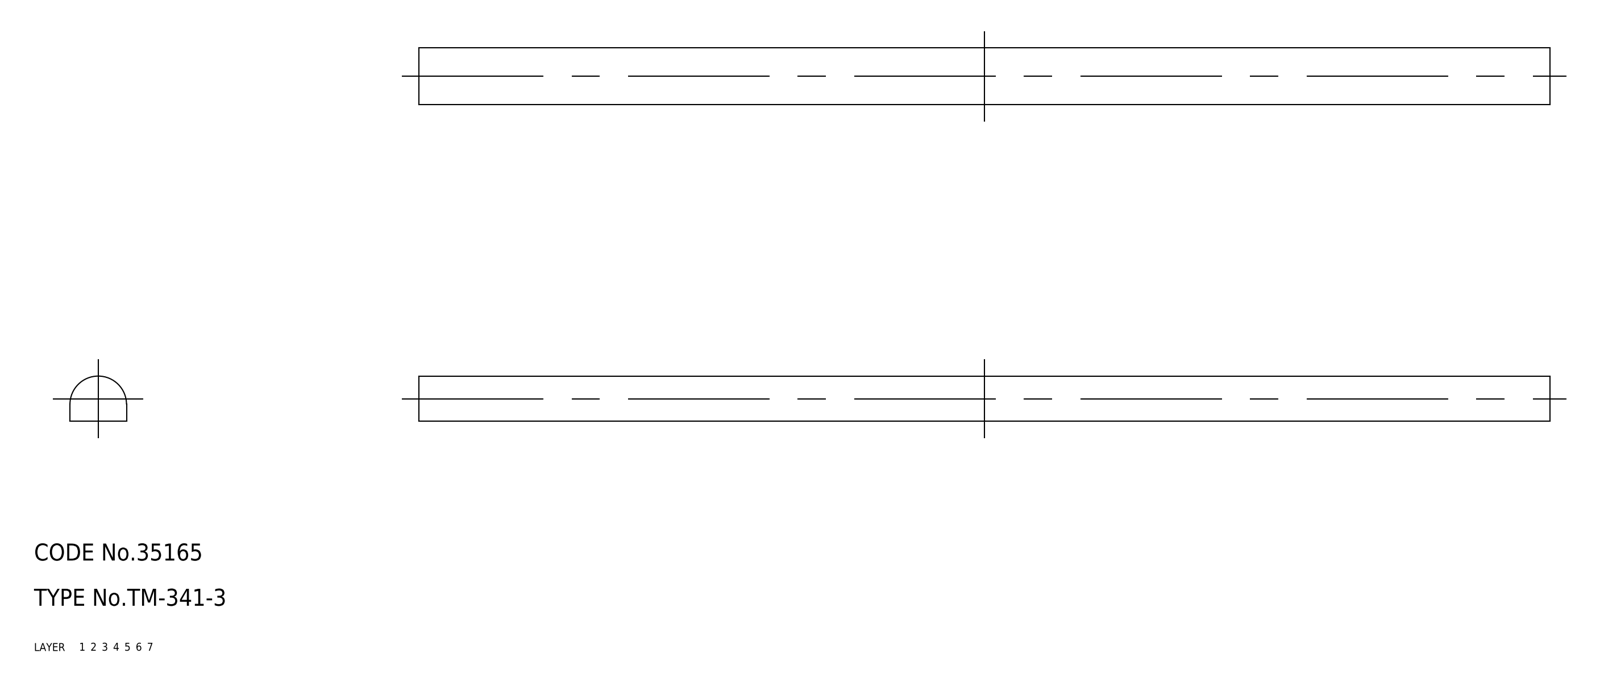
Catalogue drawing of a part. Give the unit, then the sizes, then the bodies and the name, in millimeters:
Units: millimetres
Overall size (bounding box): 200 × 10 × 8
Partial cylindrical surfaces — rounded edges, fillets, slot ends (radius × count): R5 ×1
Main face-to-face distances: 10, 200
Volume: 13 854 mm³ · Surface area: 6 480 mm²
Bodies: 1 solid, 6 faces (5 planar, 1 cylindrical, 0 other)
Part name (STEP PRODUCT): TM_341_3; rubber foam
STEP written by: SolidWorks 2015 (AUTOMOTIVE_DESIGN)
